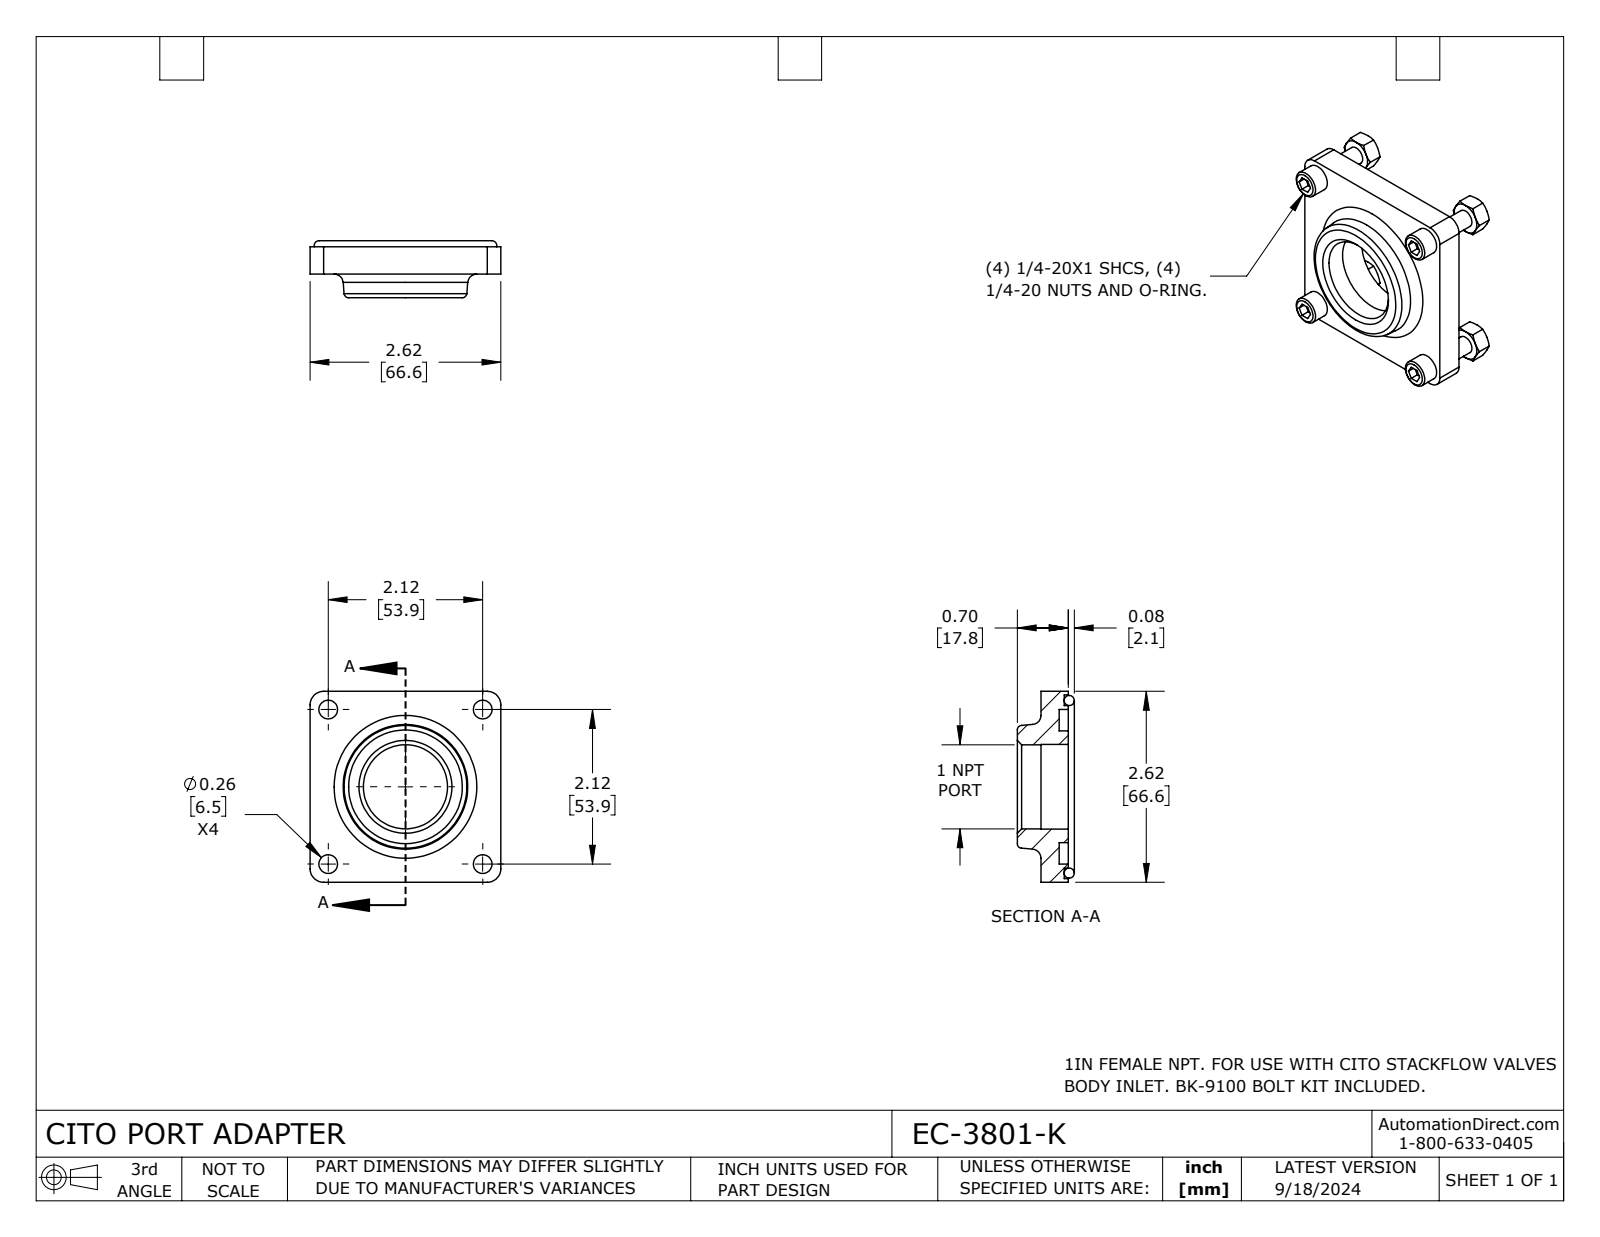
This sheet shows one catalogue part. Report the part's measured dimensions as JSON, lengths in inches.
{"part_name": "EC-3801-K", "step_written_by": "SolidWorks 2023 (CONFIG_CONTROL_DESIGN)", "units": "inches", "bodies": {"solids": 10, "faces": 218, "planar": 84, "cylindrical": 48, "other": 86}, "overall_size": [2.63, 2.624, 1.325], "volume_in3": 2.756, "surface_area_in2": 33.71, "round_holes": [[0.183, 4], [0.257, 4], [1.156, 1], [1.163, 1], [2.125, 1], [2.525, 1]], "round_bosses_or_shafts": [[0.375, 4], [0.25, 4], [2.234, 1], [1.535, 1]], "partial_cylinders_radius": [[0.187, 2], [0.188, 2]], "face_to_face_distances": [0.375, 0.125, 0.25, 2.624, 0.32, 0.07, 0.055, 0.375, 0.325, 0.575], "hole_center_spacings": [1.502, 2.124, 3.003]}
